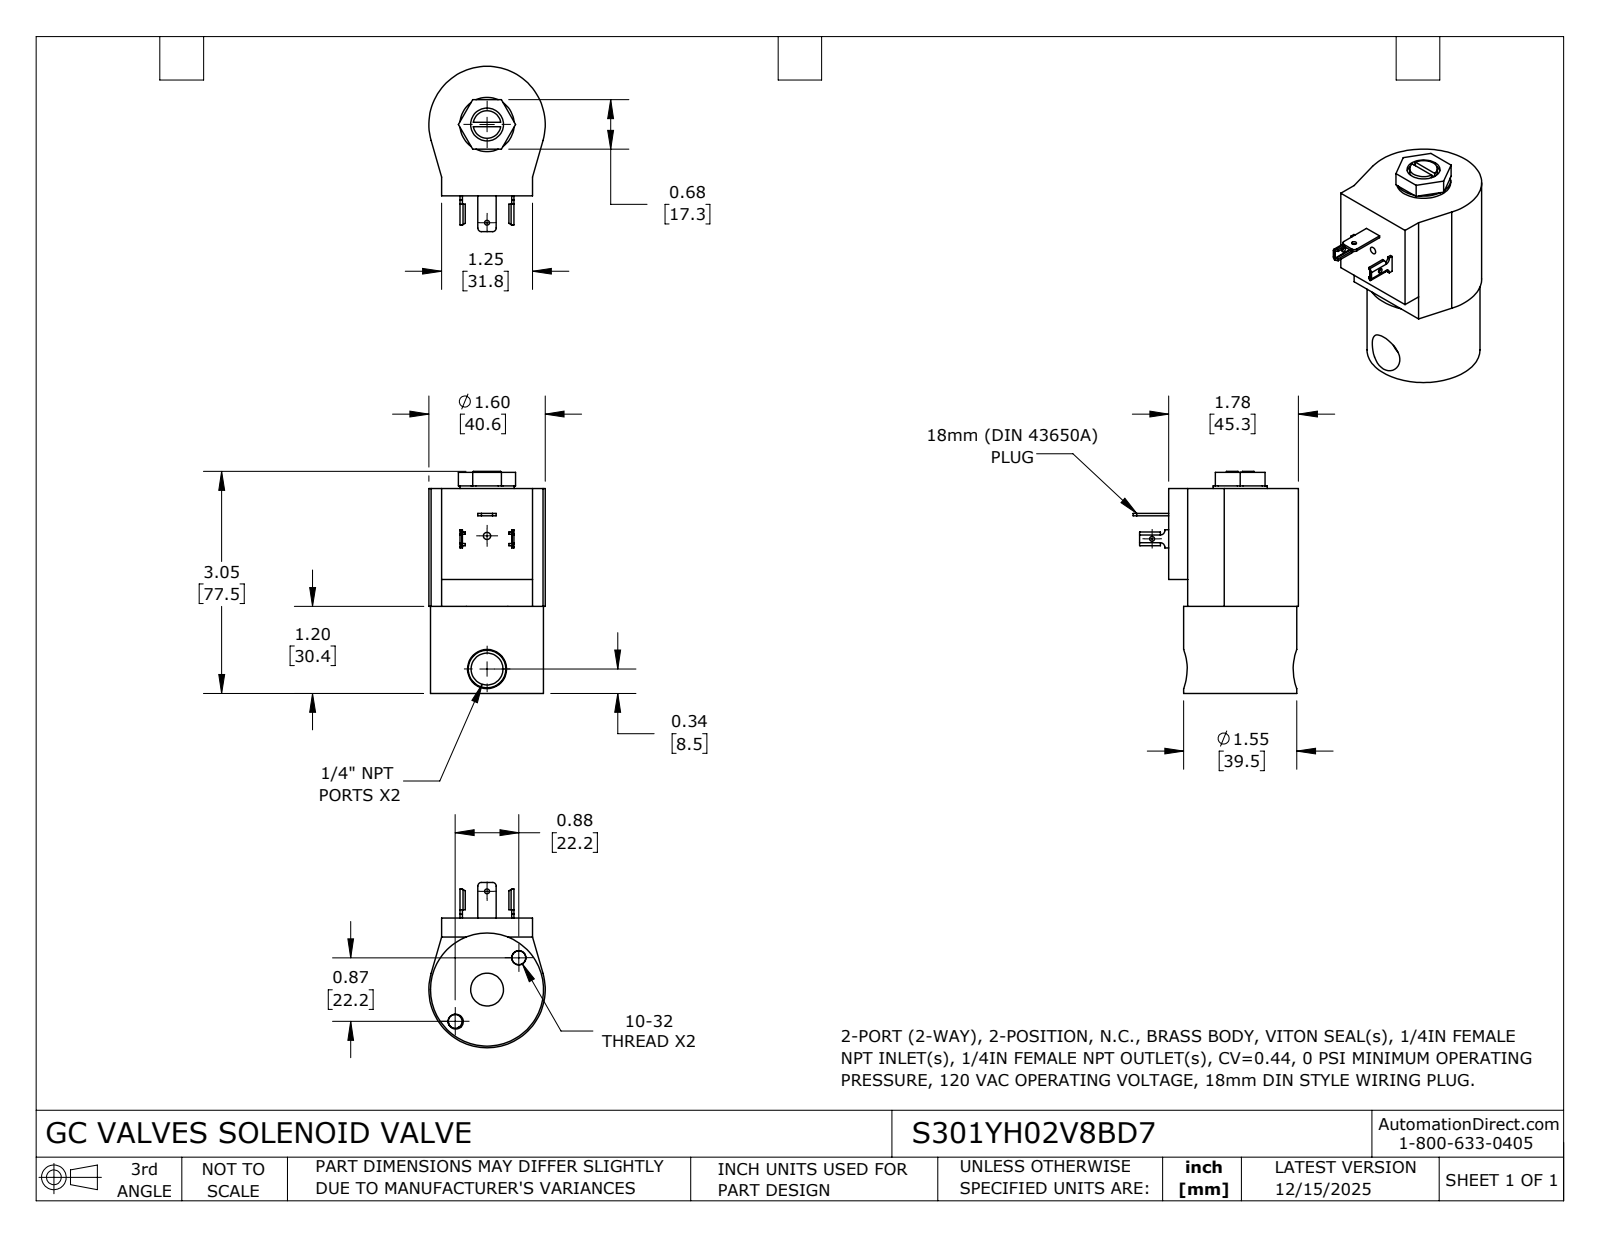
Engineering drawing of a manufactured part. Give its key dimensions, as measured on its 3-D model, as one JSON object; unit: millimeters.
{"part_name": "S301YH02V8BD7", "step_written_by": "SolidWorks 2024 (CONFIG_CONTROL_DESIGN)", "units": "millimeters", "bodies": {"solids": 2, "faces": 171, "planar": 78, "cylindrical": 71, "other": 22}, "overall_size": [77.7, 57.7, 40.6], "volume_mm3": 95600, "surface_area_mm2": 17780, "round_holes": [[4.8, 2], [1.7, 1], [1.7, 1], [2.5, 1], [11.1, 1], [11.5, 1]], "round_bosses_or_shafts": [[39.4, 1], [18.9, 1], [9.7, 1]], "partial_cylinders_radius": [[0.2, 4], [1, 4], [1.3, 2], [1.5, 2], [20.3, 1]], "face_to_face_distances": [41.1, 30.4, 71.5, 6.6, 39.8, 9.4, 31.8, 31.8, 77.2, 46.8], "hole_center_spacings": [15.7, 15.7, 25.7, 31.4, 34.3, 46.5, 46.7]}
